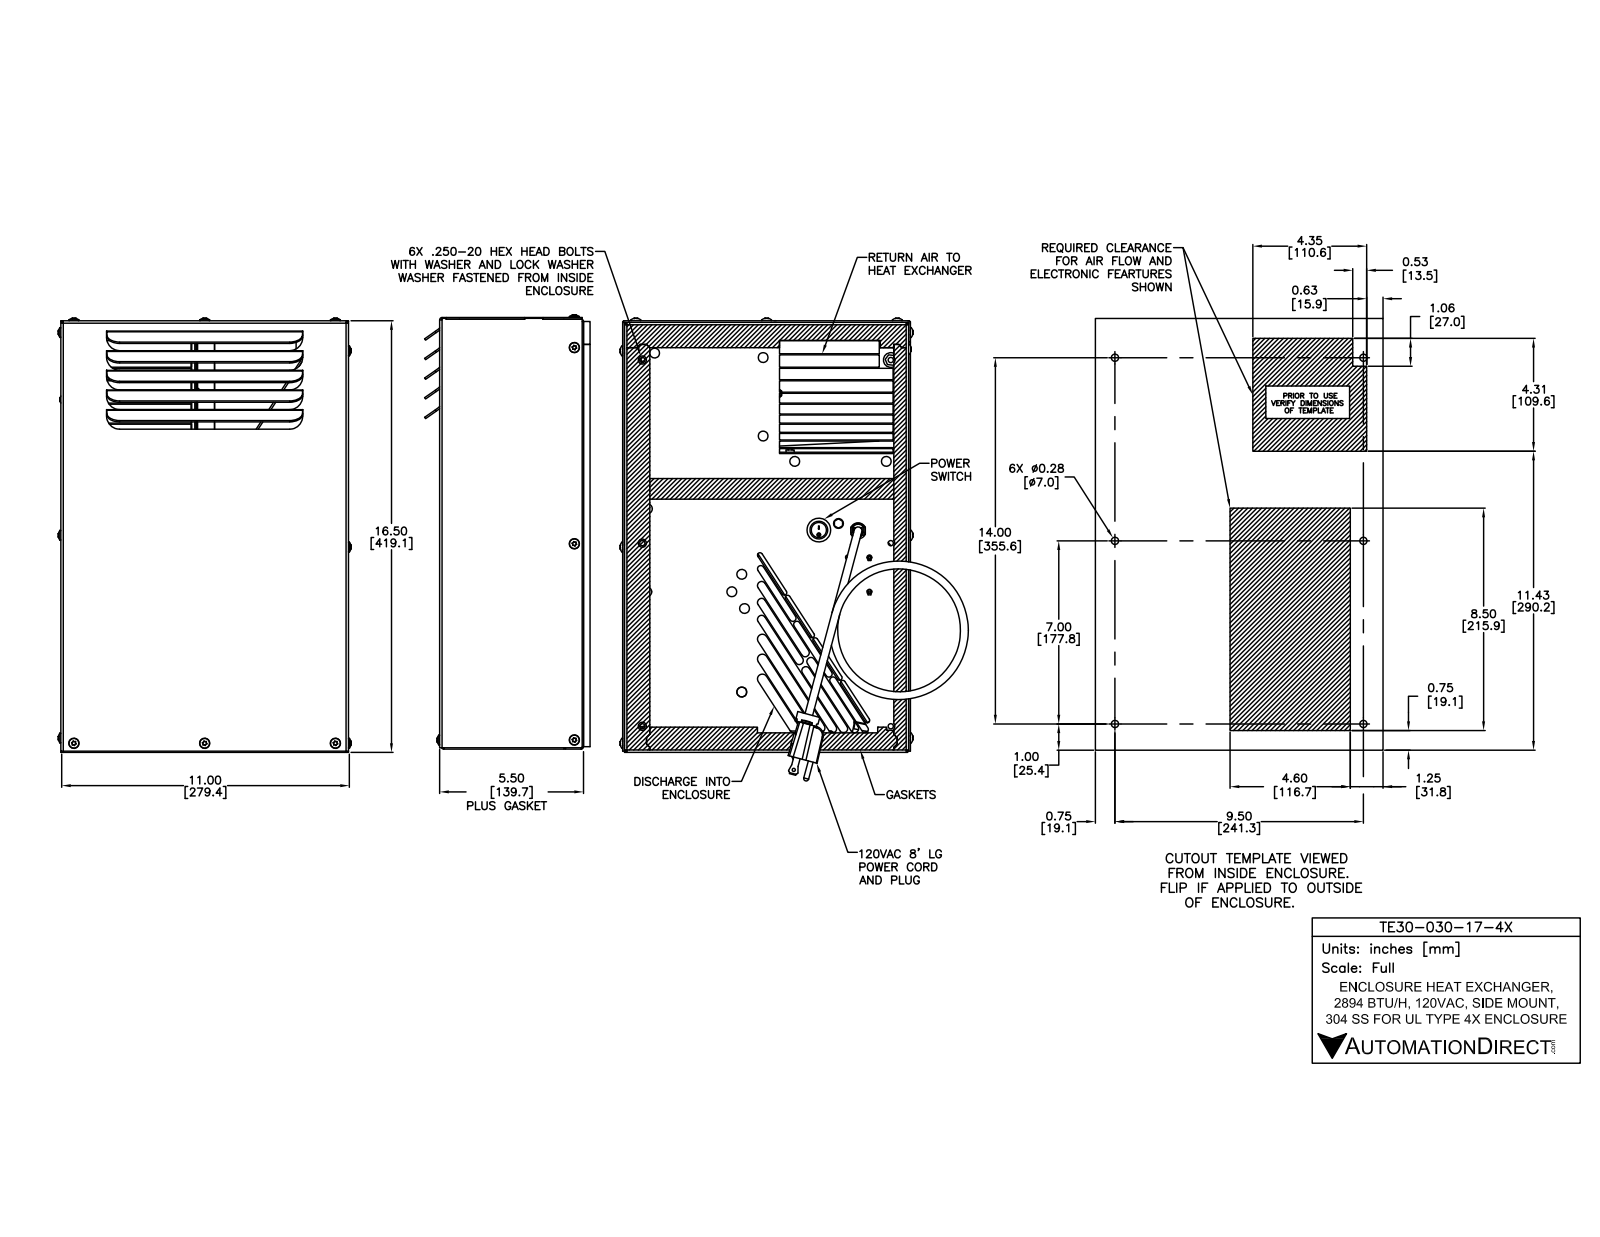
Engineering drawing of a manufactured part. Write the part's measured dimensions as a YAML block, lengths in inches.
part_name: "TE30-030-17-4X"
step_written_by: "SolidWorks 2017 (AUTOMOTIVE_DESIGN)"
units: inches
bodies: {solids: 122, faces: 3166, planar: 1807, cylindrical: 975, other: 384}
overall_size: [16.594, 11.188, 6.463]
volume: 170.6
surface_area: 3102
round_holes:
  - {diameter: 0.188, count: 23}
  - {diameter: 0.193, count: 23}
  - {diameter: 0.219, count: 19}
  - {diameter: 0.5, count: 16}
  - {diameter: 0.203, count: 9}
  - {diameter: 0.156, count: 8}
  - {diameter: 0.109, count: 7}
  - {diameter: 0.195, count: 6}
  - {diameter: 0.2, count: 6}
  - {diameter: 0.201, count: 6}
  - {diameter: 0.25, count: 6}
  - {diameter: 0.272, count: 6}
round_bosses_or_shafts:
  - {diameter: 0.27, count: 23}
  - {diameter: 0.19, count: 15}
  - {diameter: 0.564, count: 6}
  - {diameter: 0.44, count: 6}
  - {diameter: 0.344, count: 6}
  - {diameter: 0.326, count: 6}
  - {diameter: 0.325, count: 6}
  - {diameter: 0.311, count: 6}
partial_cylinders:
  - {radius: 0.01, count: 84}
  - {radius: 0.015, count: 84}
  - {radius: 0.031, count: 59}
  - {radius: 0.093, count: 46}
  - {radius: 0.101, count: 18}
  - {radius: 0.06, count: 17}
  - {radius: 0.094, count: 13}
  - {radius: 0.125, count: 12}
face_to_face_distances: [0.062, 0.062, 10.871, 5.5, 5.376, 5.438, 5.438, 10.933, 10.809, 1.083]
hole_center_spacings: [1.25, 2.5, 3.75, 1.296, 1.205, 2.546, 0.06, 3.25]
